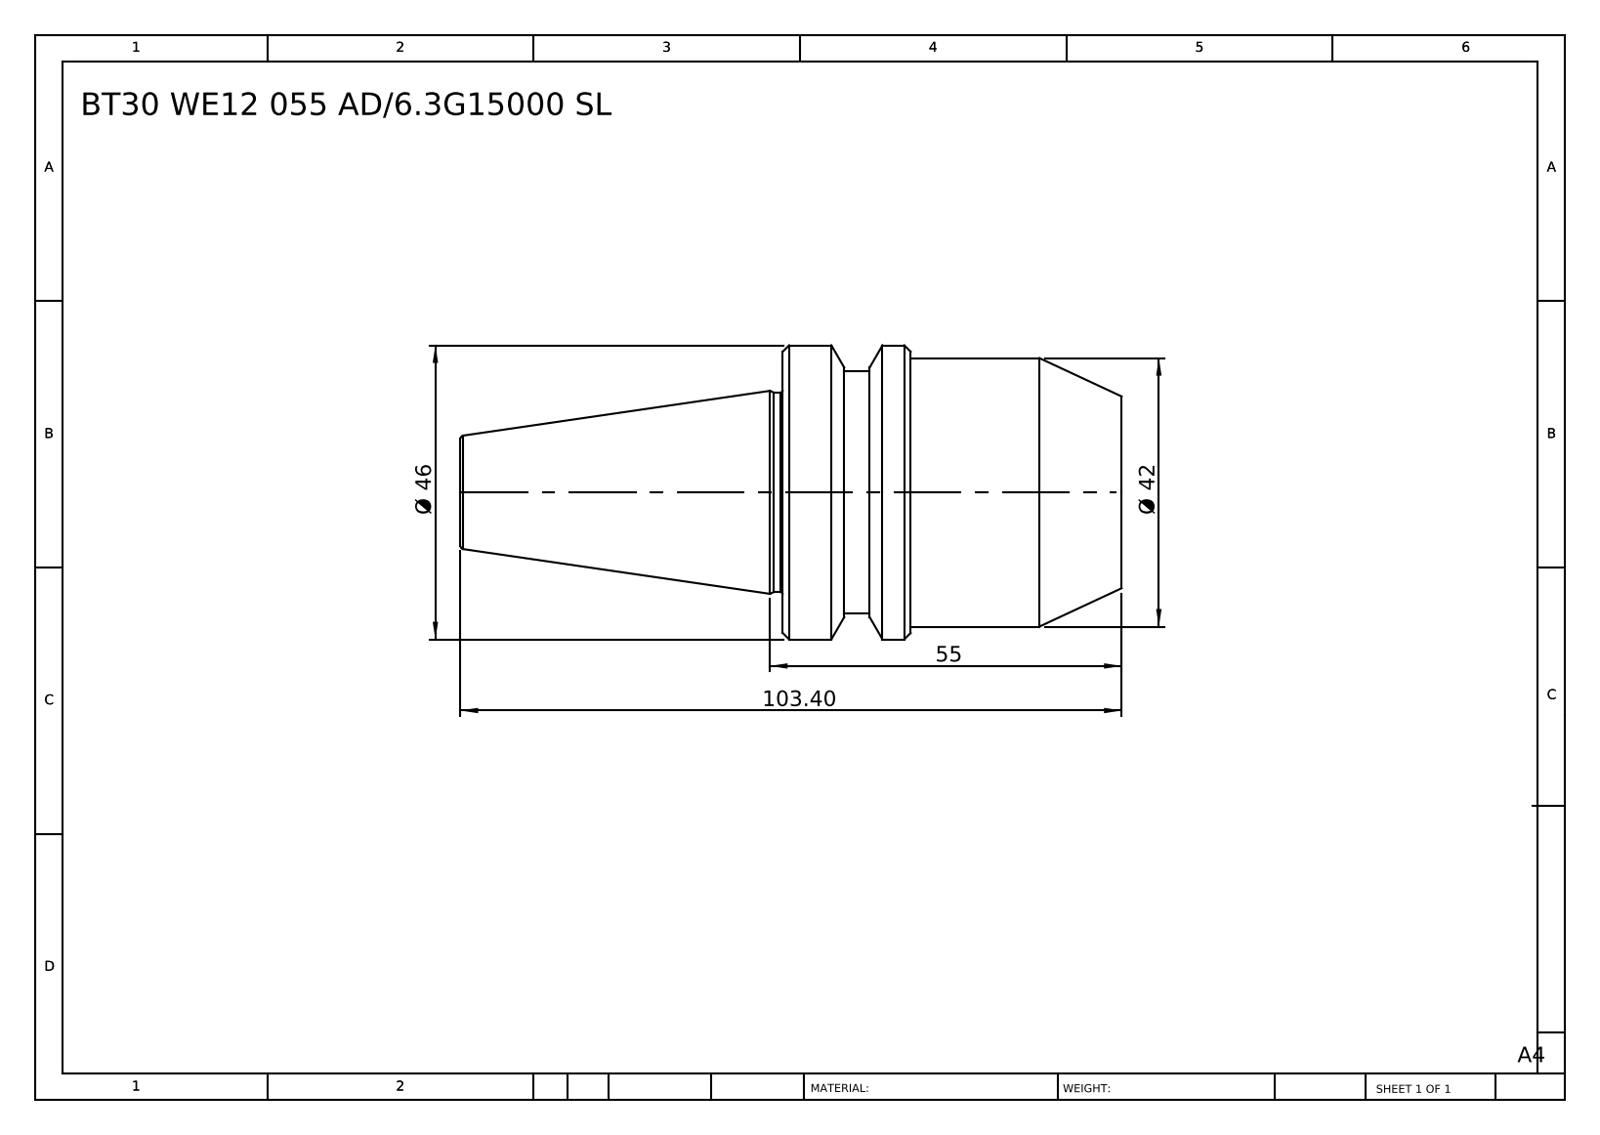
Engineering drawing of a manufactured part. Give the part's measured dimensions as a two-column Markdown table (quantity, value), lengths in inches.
| quantity | value |
| --- | --- |
| part name | BT30 WE12 055 AD-6.3G15000 SL |
| STEP written by | SolidWorks 2014 (CONFIG_CONTROL_DESIGN) |
| units | inches |
| bodies | 1 solid, 34 faces (6 planar, 10 cylindrical, 18 other) |
| overall size | 4.071 × 1.811 × 1.811 |
| volume | 5.888 in³ |
| surface area | 21.08 in² |
| round bosses / shafts (diameter × count) | 1.811 × 1, 1.654 × 1, 1.496 × 1, 1.228 × 1 |
| main face-to-face distances | 2.087, 4.071, 1.984, 1.299, 0.787, 2.772, 1.709, 0.409, 0.378, 2.362 |
